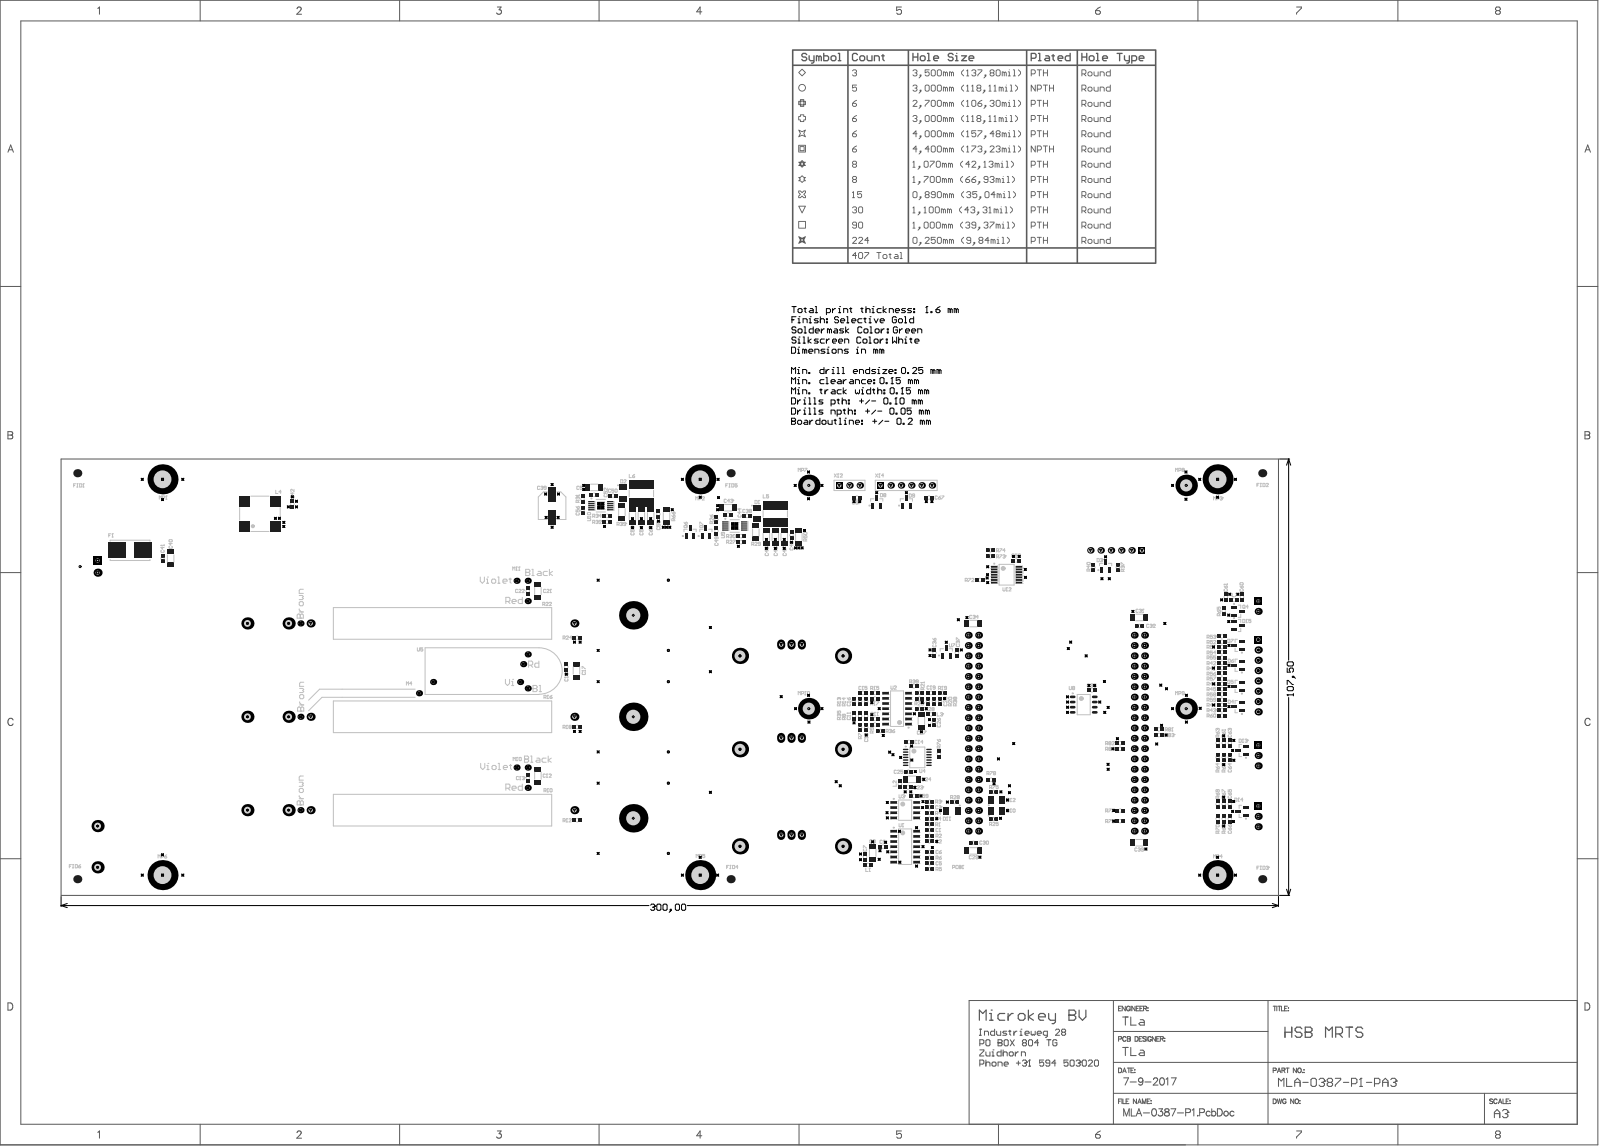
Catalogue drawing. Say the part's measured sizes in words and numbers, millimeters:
The part is named "PCB; Board; R84; 836463272 (+8 more)". Its 3-D file was written by "Open CASCADE 6.8 (AUTOMOTIVE_DESIGN)". It is 560 solids with 10210 faces: 7793 planar, 1712 cylindrical and 705 other. Overall it measures 300 by 107.5 by 53.19 millimeters. Its volume is 137 834 cubic millimeters and its surface area 131 081 square millimeters. Round holes: 89 of diameter 1, 36 of diameter 1.1, 15 of diameter 0.89, 11 of diameter 3, 8 of diameter 1.07, 8 of diameter 1.7, 6 of diameter 2.3, 6 of diameter 2.46, 6 of diameter 2.7, 6 of diameter 4, 6 of diameter 4.4, 4 of diameter 1.57. Round bosses or shafts: 14 of diameter 1.8, 6 of diameter 6, 6 of diameter 4.2, 6 of diameter 0.85, 4 of diameter 4.35, 4 of diameter 2.8, 3 of diameter 7.9, 1 of diameter 12.2. Partial cylindrical surfaces (rounded edges, fillets, slot ends): 178 of radius 0.1, 117 of radius 0.13, 74 of radius 0.2, 18 of radius 0.3, 12 of radius 0.3, 12 of radius 0.75, 11 of radius 0.5, 10 of radius 0.15. The main face-to-face distances are 1.85, 10.39, 12.24, 1.6, 11.99, 13.84, 1.5, 21.8, 5.75, 22.75. The hole center spacings are 12.23, 17.3, 23, 18.5, 10.16, 15.5, 25, 31.35.
